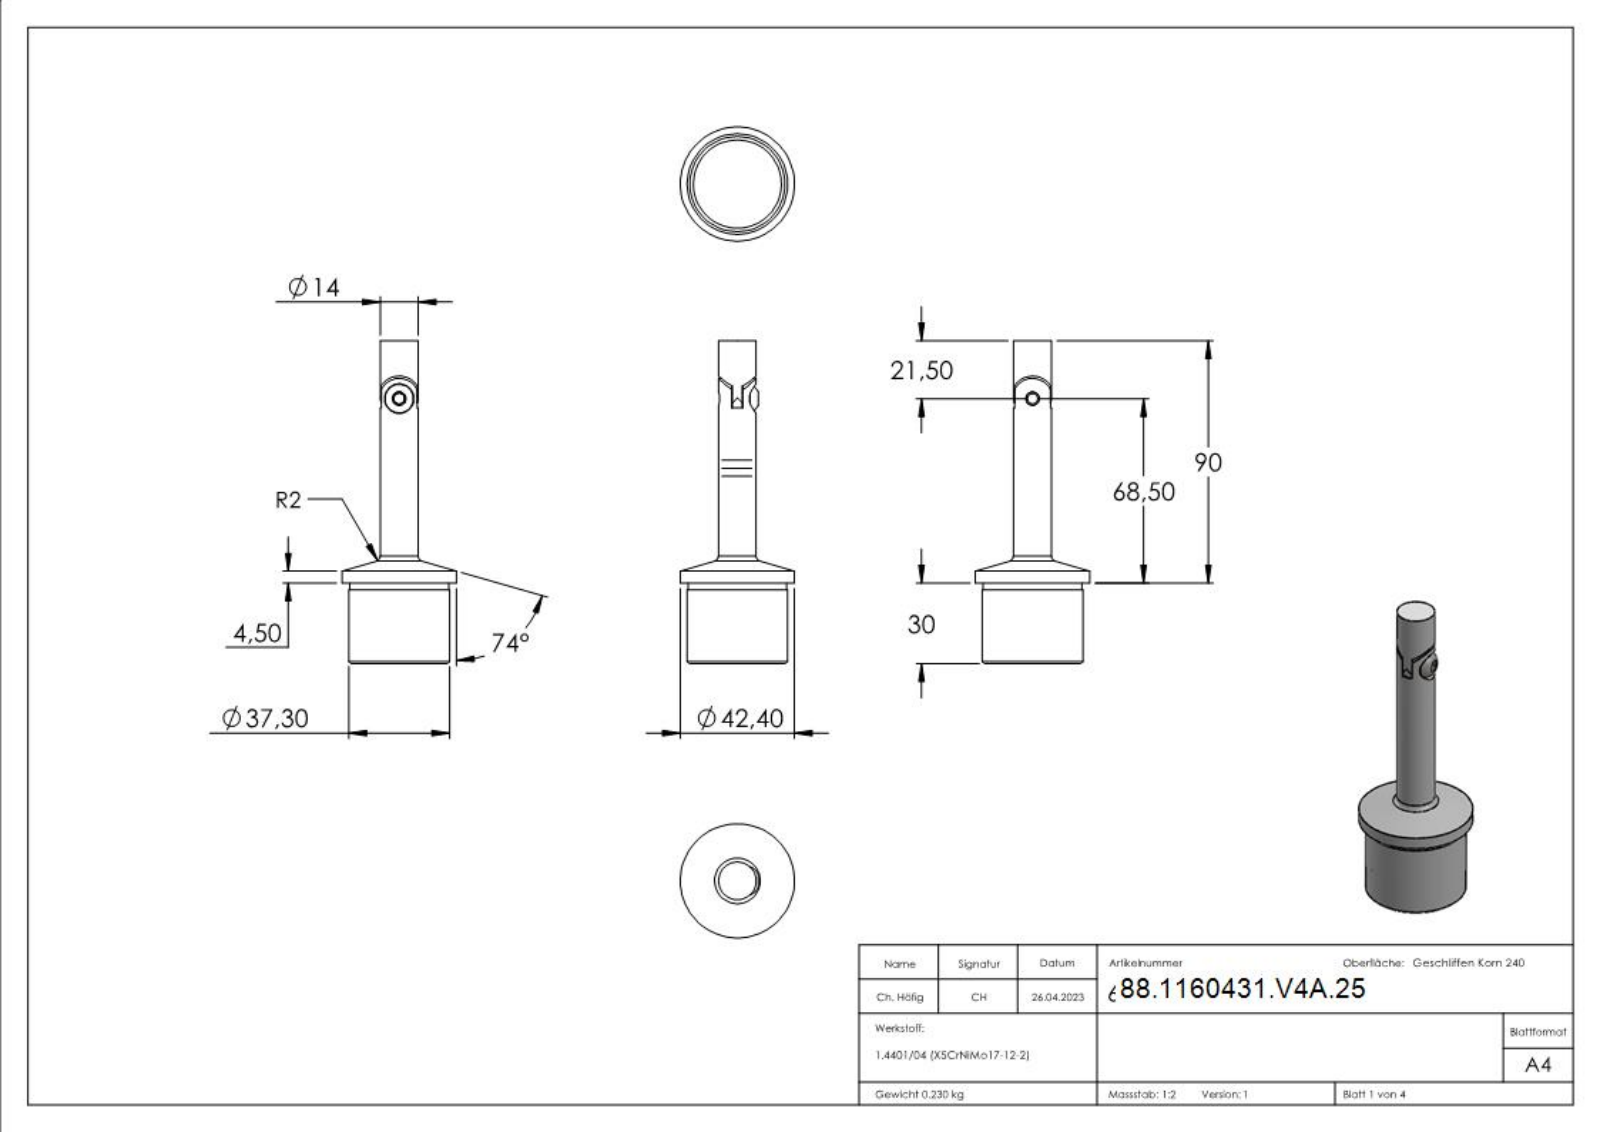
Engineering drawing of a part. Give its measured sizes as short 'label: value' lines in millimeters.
name: 60431-V4A-25 Teil2; 60431-V4A-25; 60431-V4A-25 Teil1_60431-V4A-25 Teil1; 60431-V4A-25 Teil3_M6x10
written by: SolidWorks 2018 (CONFIG_CONTROL_DESIGN)
unit: mm
bodies: 3 solids, 305 faces (152 planar, 47 cylindrical, 106 other)
size: 120 × 42.4 × 42.4
volume: 28 727 mm³; area: 15 164 mm²
holes: 1× ⌀5, 1× ⌀6.5, 1× ⌀6.6, 1× ⌀11, 1× ⌀32.7
bosses: 1× ⌀42.4, 1× ⌀37.3, 1× ⌀36.7, 1× ⌀14, 1× ⌀10.5, 1× ⌀4.77
rounds: 2× R7, 1× R7.44, 1× R8, 1× R16.85
face distances: 2.5, 4, 90, 30, 120, 3.88, 3.75, 3.87, 6.5, 6.37
